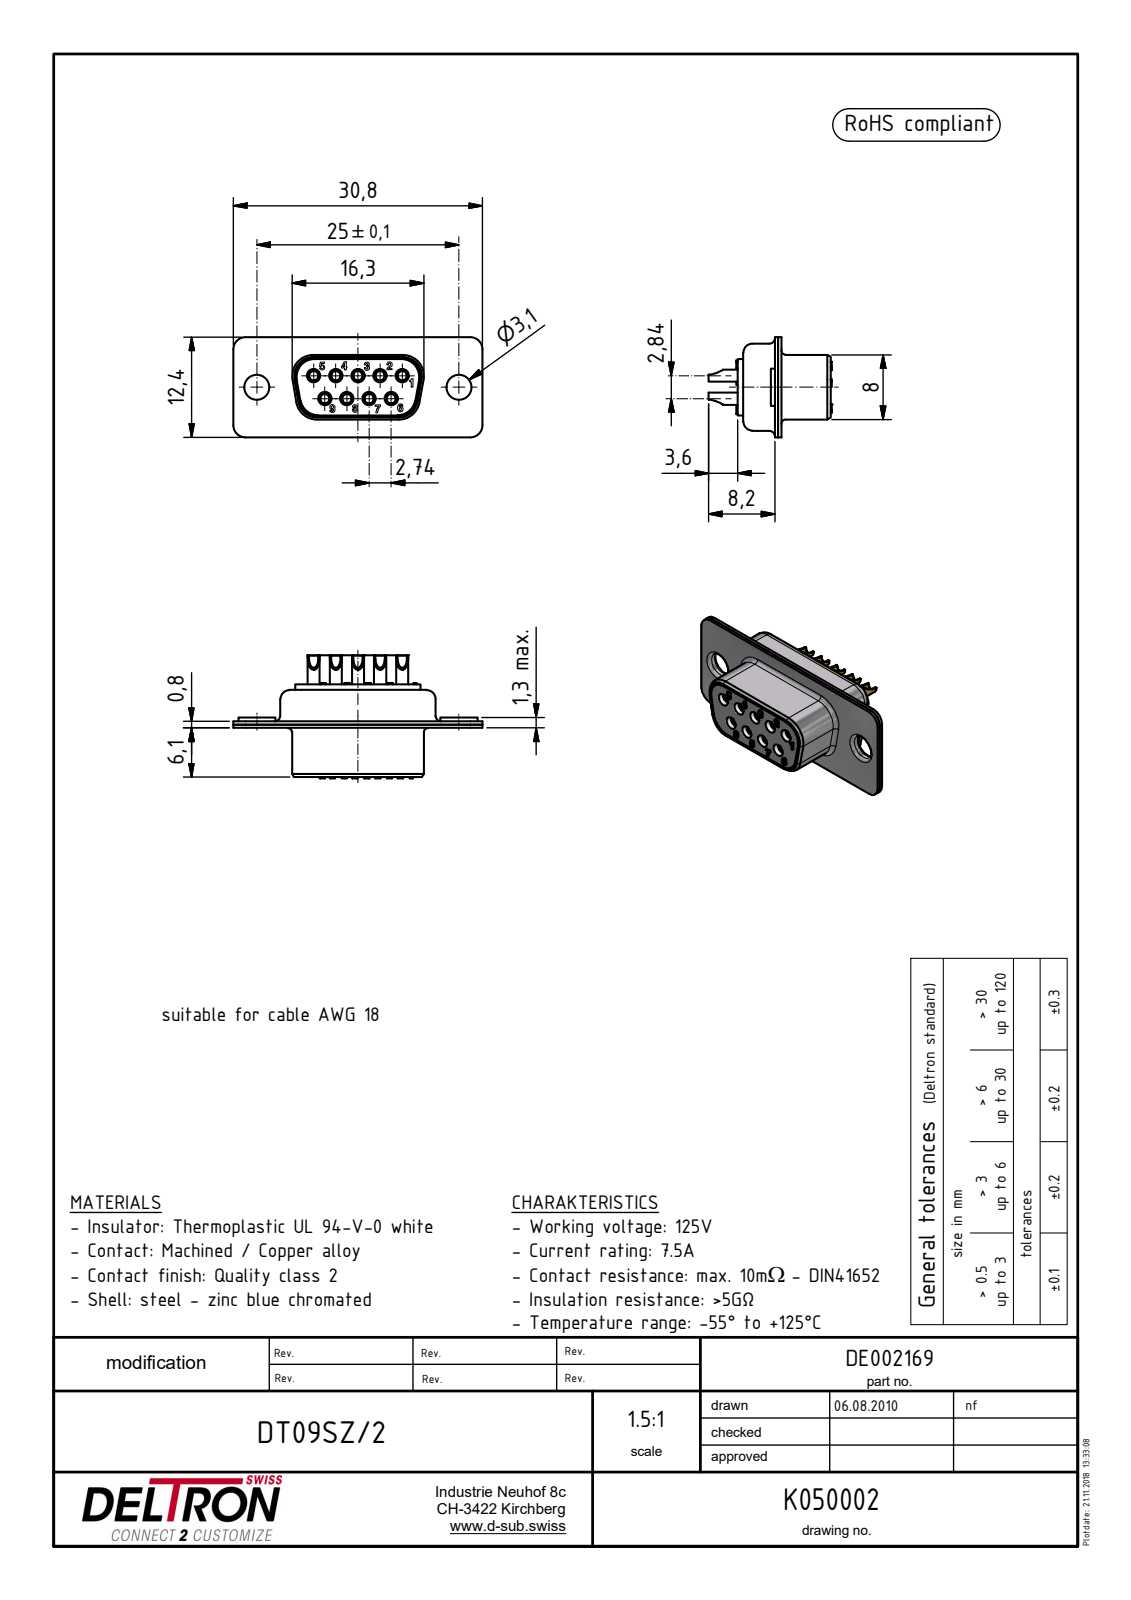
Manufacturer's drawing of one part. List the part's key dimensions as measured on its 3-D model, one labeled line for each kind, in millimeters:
Part name (STEP PRODUCT): N00402_BG; R+B00142_BG; R+B00136_BG; R+B00894_BG (+1 more)
STEP written by: Autodesk Inventor 2015 (AUTOMOTIVE_DESIGN)
Units: millimetres
Bodies: 12 solids, 752 faces (348 planar, 221 cylindrical, 183 other)
Overall size (bounding box): 30.8 × 15.25 × 12.4
Volume: 1 601 mm³ · Surface area: 4 413 mm²
Round holes (diameter × count): ⌀1.15 ×9, ⌀1.2 ×9, ⌀1.92 ×9, ⌀2.3 ×9, ⌀0.24 ×2, ⌀0.28 ×2, ⌀0.34 ×2, ⌀3.1 ×2, ⌀4.06 ×2
Round bosses / shafts (diameter × count): ⌀2.23 ×9, ⌀1.96 ×9, ⌀1.7 ×9, ⌀1.6 ×9, ⌀1.5 ×9, ⌀4.6 ×2, ⌀3.9 ×2
Partial cylindrical surfaces — rounded edges, fillets, slot ends (radius × count): R2 ×12, R0.7 ×8, R1.1 ×8, R2.2 ×8, R0.5 ×4, R0.9 ×4, R1 ×4, R1.2 ×4
Main face-to-face distances: 0.4, 0.8, 1.4, 10.2, 0.5, 1.2, 1.3, 9, 7.1, 9.8
Hole centre spacings: 3.15, 2.74, 5, 5.48, 7.42, 8.22, 1.98, 7.16
